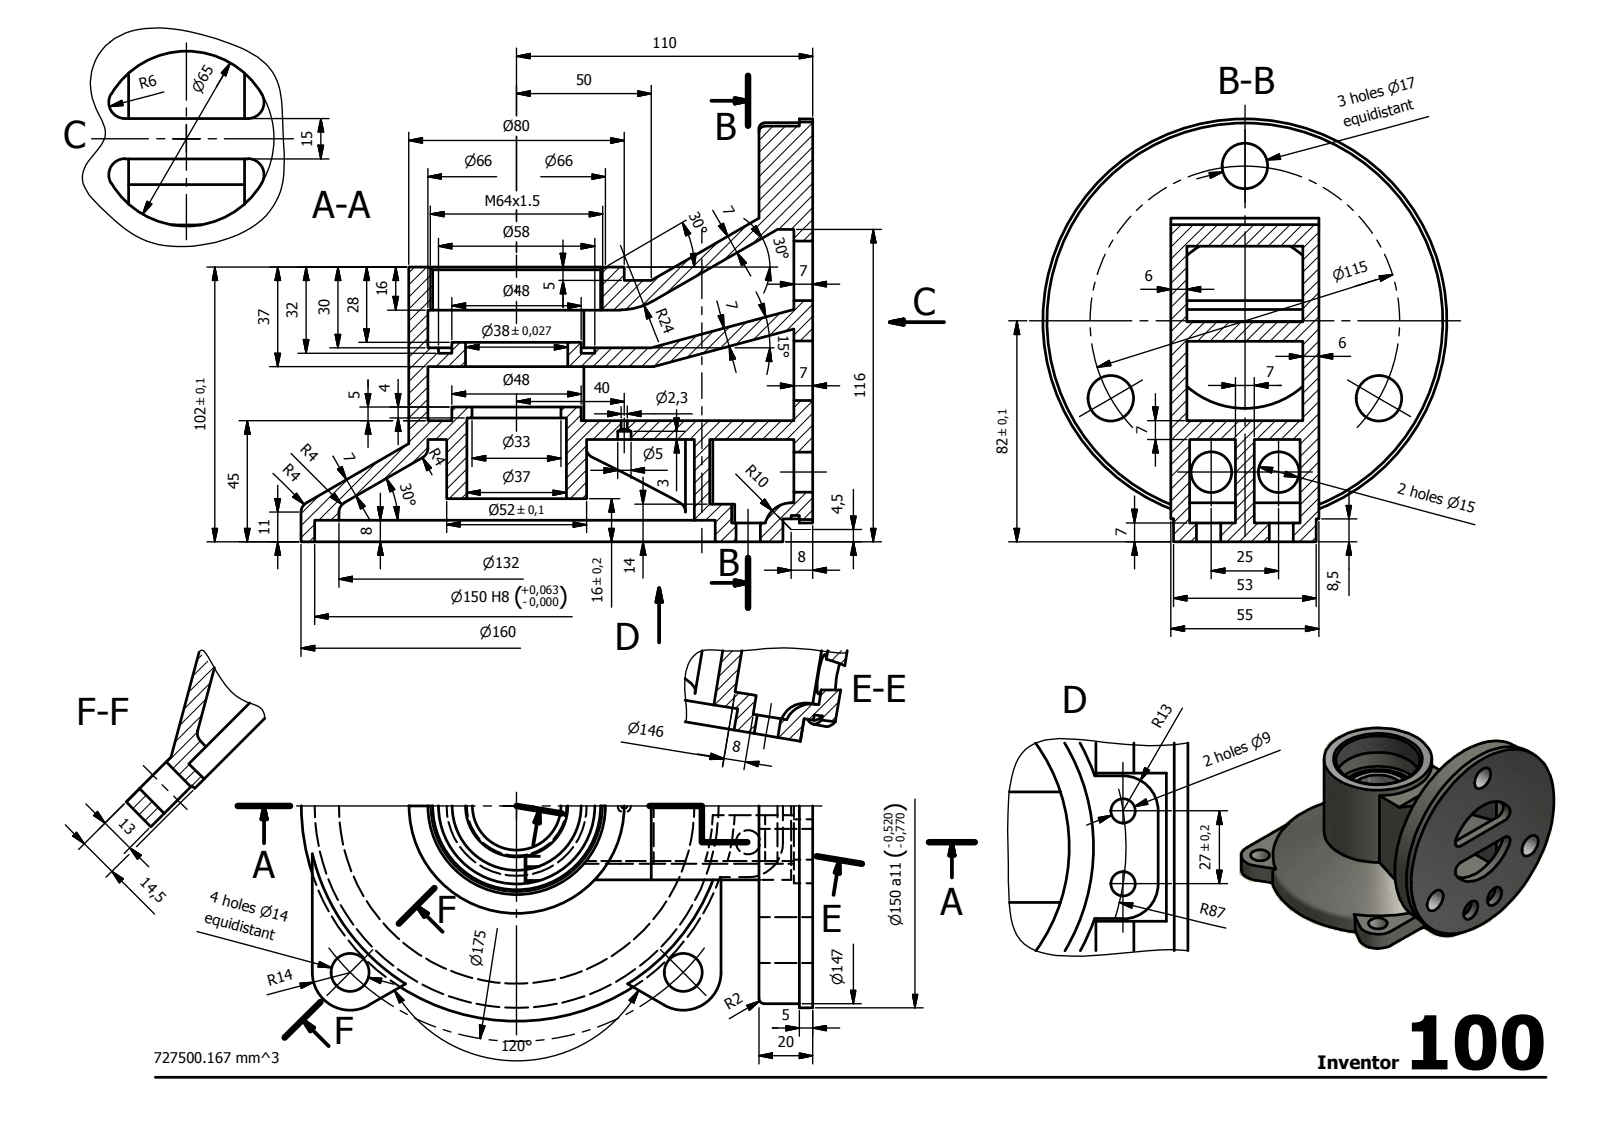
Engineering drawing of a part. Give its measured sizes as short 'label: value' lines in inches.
written by: Autodesk Inventor 2014 (AUTOMOTIVE_DESIGN)
unit: in
bodies: 1 solid, 135 faces (76 planar, 49 cylindrical, 10 other)
size: 7.48 × 6.299 × 6.181
volume: 44.39 in³; area: 283.6 in²
holes: 4× ⌀0.551, 3× ⌀0.669, 2× ⌀0.354, 2× ⌀0.591, 1× ⌀0.091, 1× ⌀0.197, 1× ⌀1.299, 1× ⌀1.457, 1× ⌀1.496, 1× ⌀2.283, 1× ⌀2.456, 1× ⌀5.197
bosses: 1× ⌀6.299, 1× ⌀5.906, 1× ⌀5.787, 1× ⌀3.15, 1× ⌀2.047, 1× ⌀1.89
rounds: 4× R0.236, 4× R0.551, 2× R0.512, 1× R0.394, 1× R0.945, 1× R1.28, 1× R1.299, 1× R2.874
face distances: 0.276, 0.787, 1.929, 0.236, 1.457, 1.063, 1.181, 2.165, 0.256, 2.244
hole spacings: 3.445, 4.872, 1.821, 1.885, 2.127, 2.583, 2.679, 3.115
